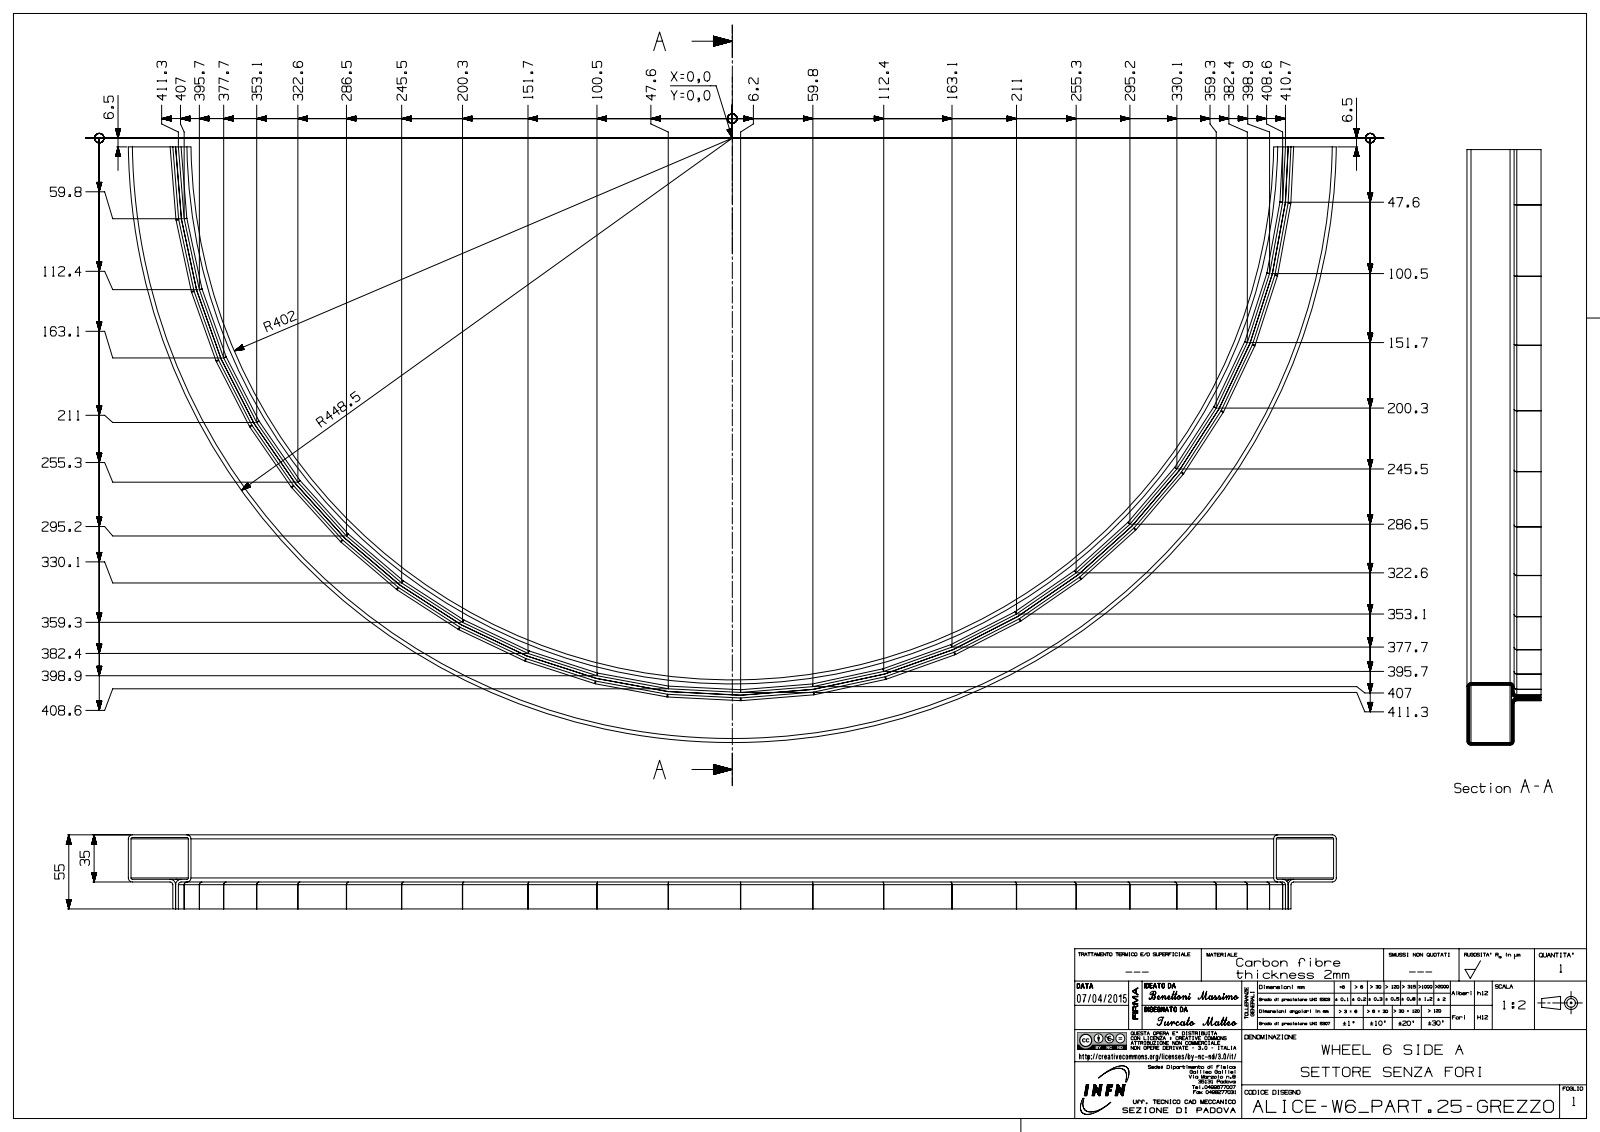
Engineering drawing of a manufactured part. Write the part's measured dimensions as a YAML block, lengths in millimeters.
part_name: "turc0EF8EEE3l0sa"
step_written_by: "SIEMENS PLM Software NX 8.5 (AP203_CONFIGURATION_CONTROLLED_3D_DESIGN_OF_MECHANICAL_PARTS_AND_ASSEMBLIES_MIM_LF)"
units: millimeters
bodies: {solids: 1, faces: 398, planar: 106, cylindrical: 192, other: 100}
overall_size: [896.91, 442, 55]
volume: 496927
surface_area: 502845
partial_cylinders:
  - {radius: 4, count: 94}
  - {radius: 2, count: 71}
  - {radius: 4.1, count: 23}
  - {radius: 402, count: 1}
  - {radius: 404, count: 1}
  - {radius: 446.5, count: 1}
  - {radius: 448.5, count: 1}
face_to_face_distances: [2, 33, 2.1, 31, 35, 4.1, 55, 53, 22, 20]
